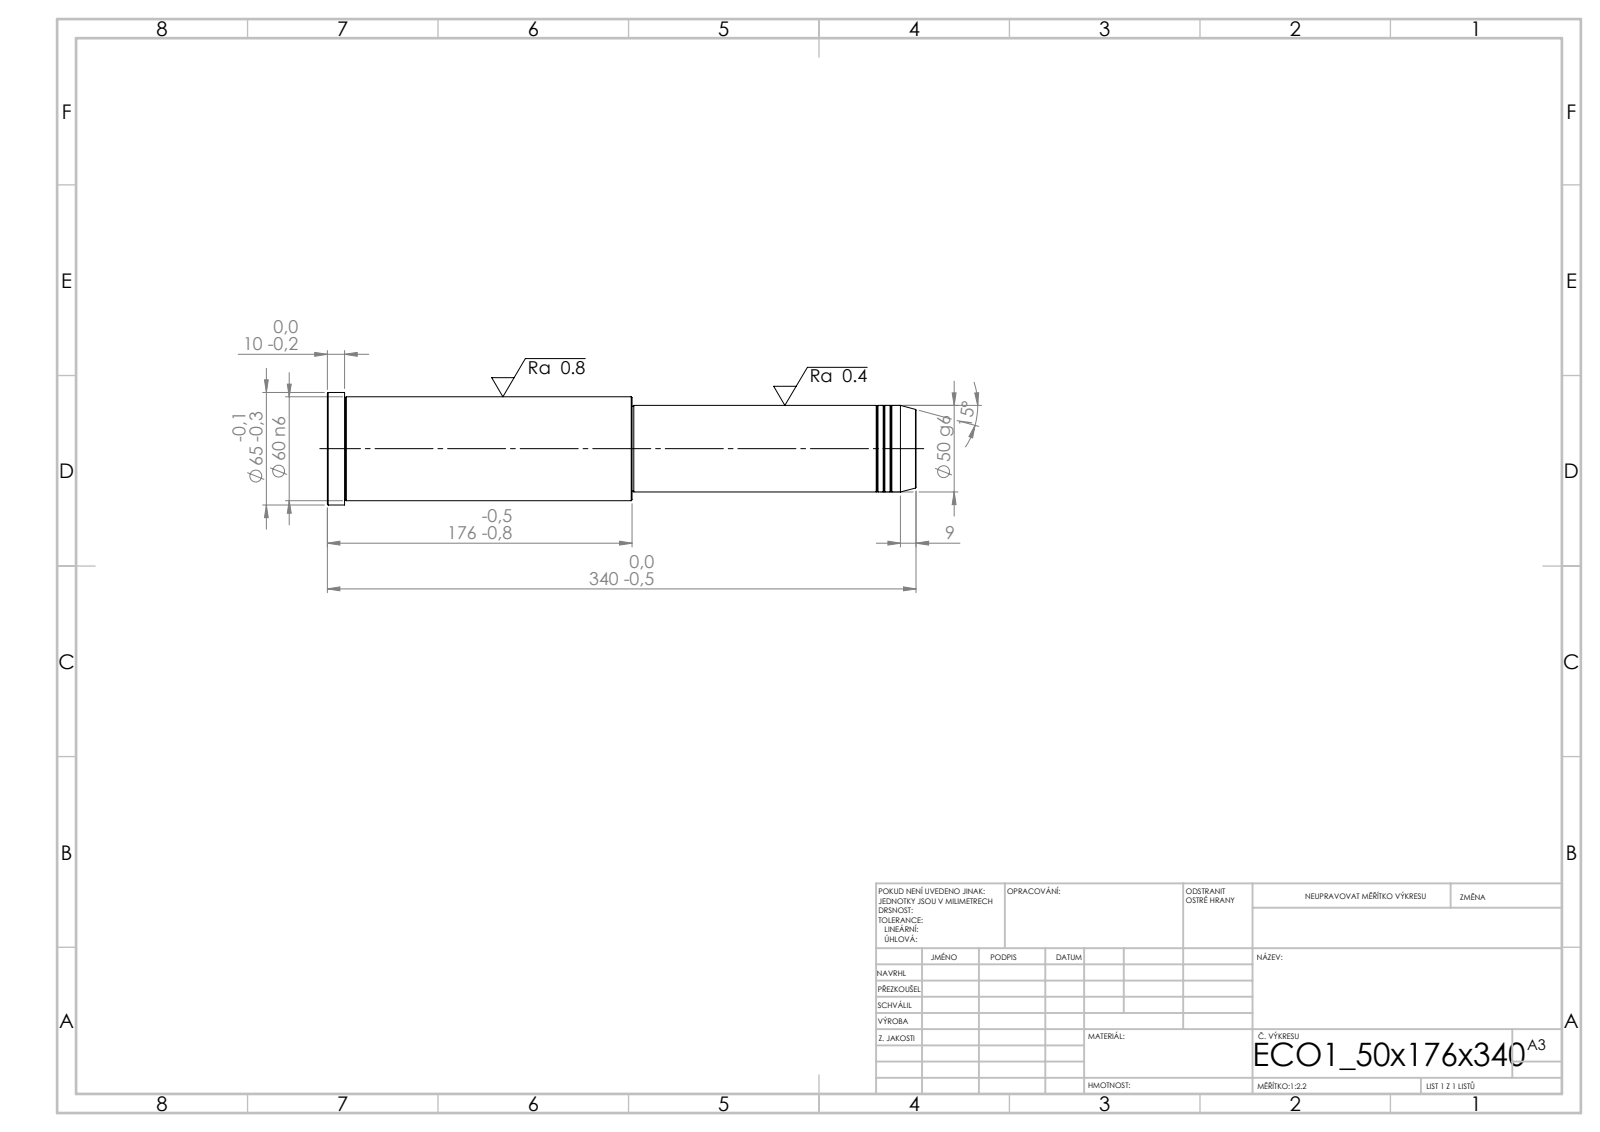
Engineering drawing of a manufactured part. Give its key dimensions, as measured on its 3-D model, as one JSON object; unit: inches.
{"step_written_by": "SolidWorks 2019 (CONFIG_CONTROL_DESIGN)", "units": "inches", "bodies": {"solids": 1, "faces": 43, "planar": 5, "cylindrical": 14, "other": 24}, "overall_size": [13.386, 2.559, 2.559], "volume_in3": 50.19, "surface_area_in2": 101.9, "round_bosses_or_shafts": [[2.559, 1], [2.362, 1], [1.969, 1], [1.929, 1]], "face_to_face_distances": [13.386, 6.457, 6.929, 12.992, 6.535, 0.394, 6.417, 0.039, 6.575, 6.969]}
